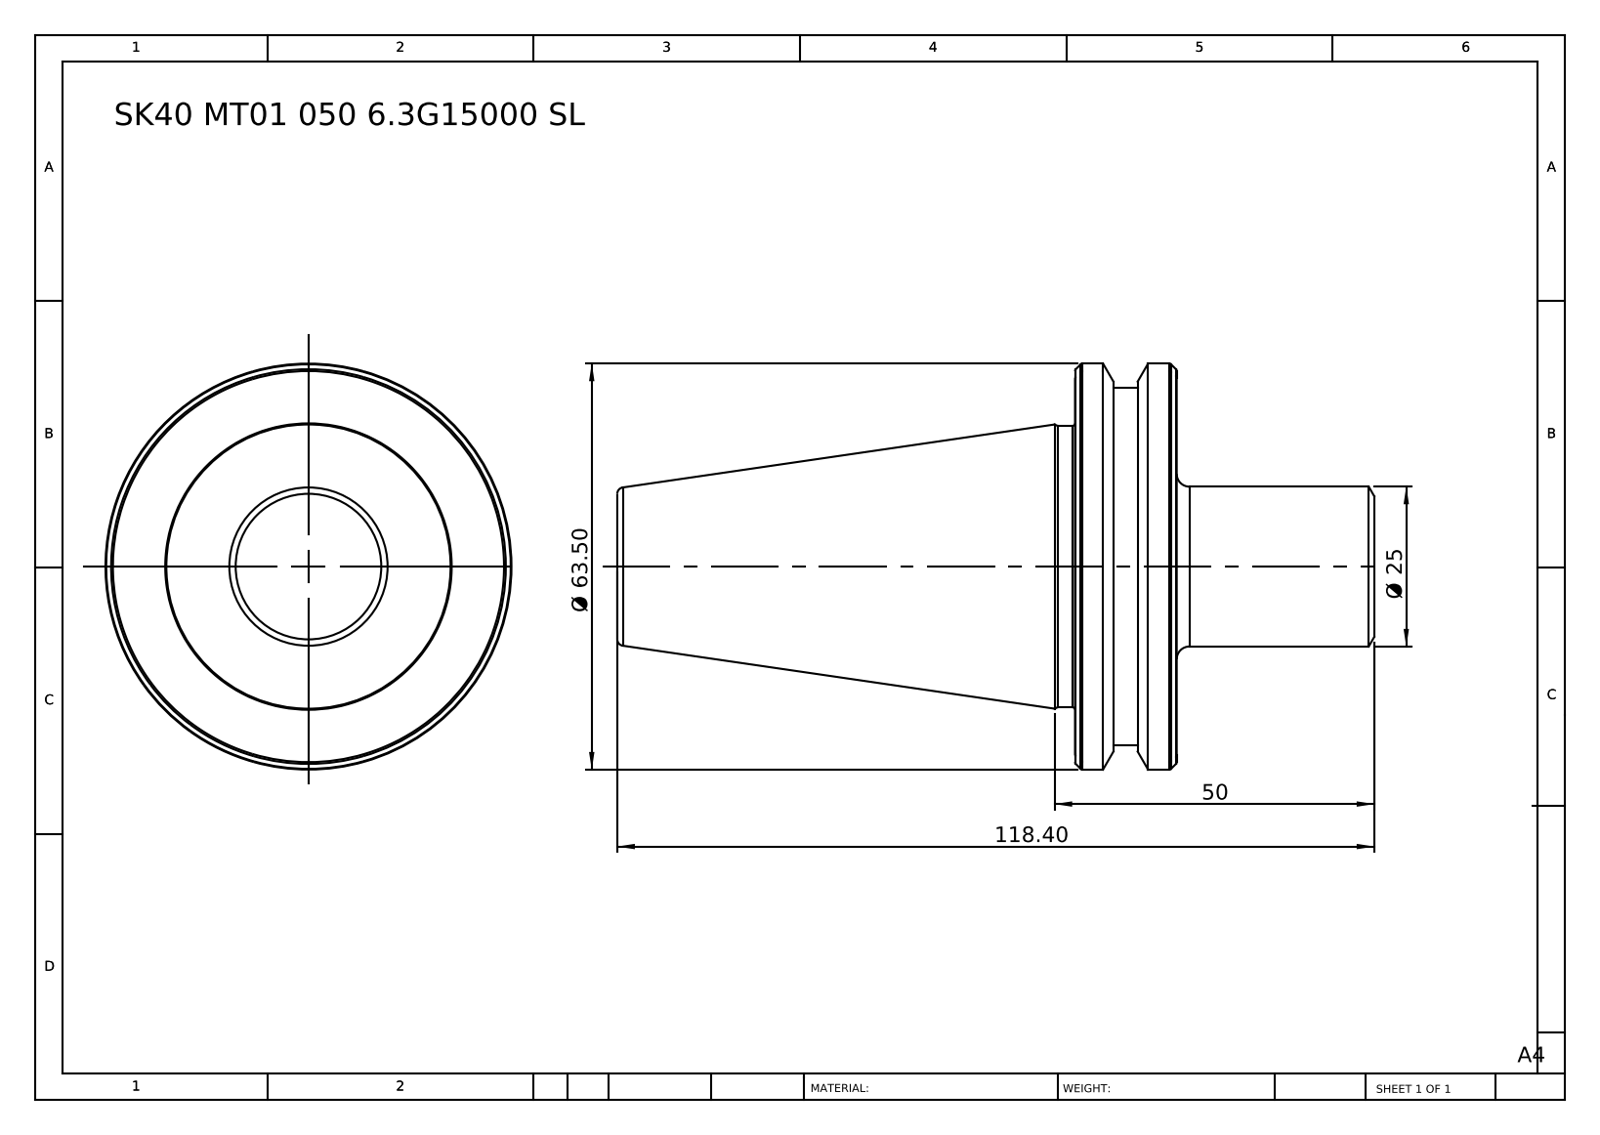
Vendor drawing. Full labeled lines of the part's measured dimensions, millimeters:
Part name (STEP PRODUCT): SK 40 MT01 050 6.3G15000 SL
STEP written by: SolidWorks 2014 (CONFIG_CONTROL_DESIGN)
Units: millimetres
Bodies: 1 solid, 64 faces (6 planar, 10 cylindrical, 48 other)
Overall size (bounding box): 118.4 × 63.5 × 63.5
Volume: 132 291 mm³ · Surface area: 19 245 mm²
Round bosses / shafts (diameter × count): ⌀63.5 ×1, ⌀56 ×1, ⌀44 ×1, ⌀25 ×1
Main face-to-face distances: 15.9, 87.5, 71.6, 30.9, 46.8, 118.4, 40.8, 9.9, 6, 77.6
